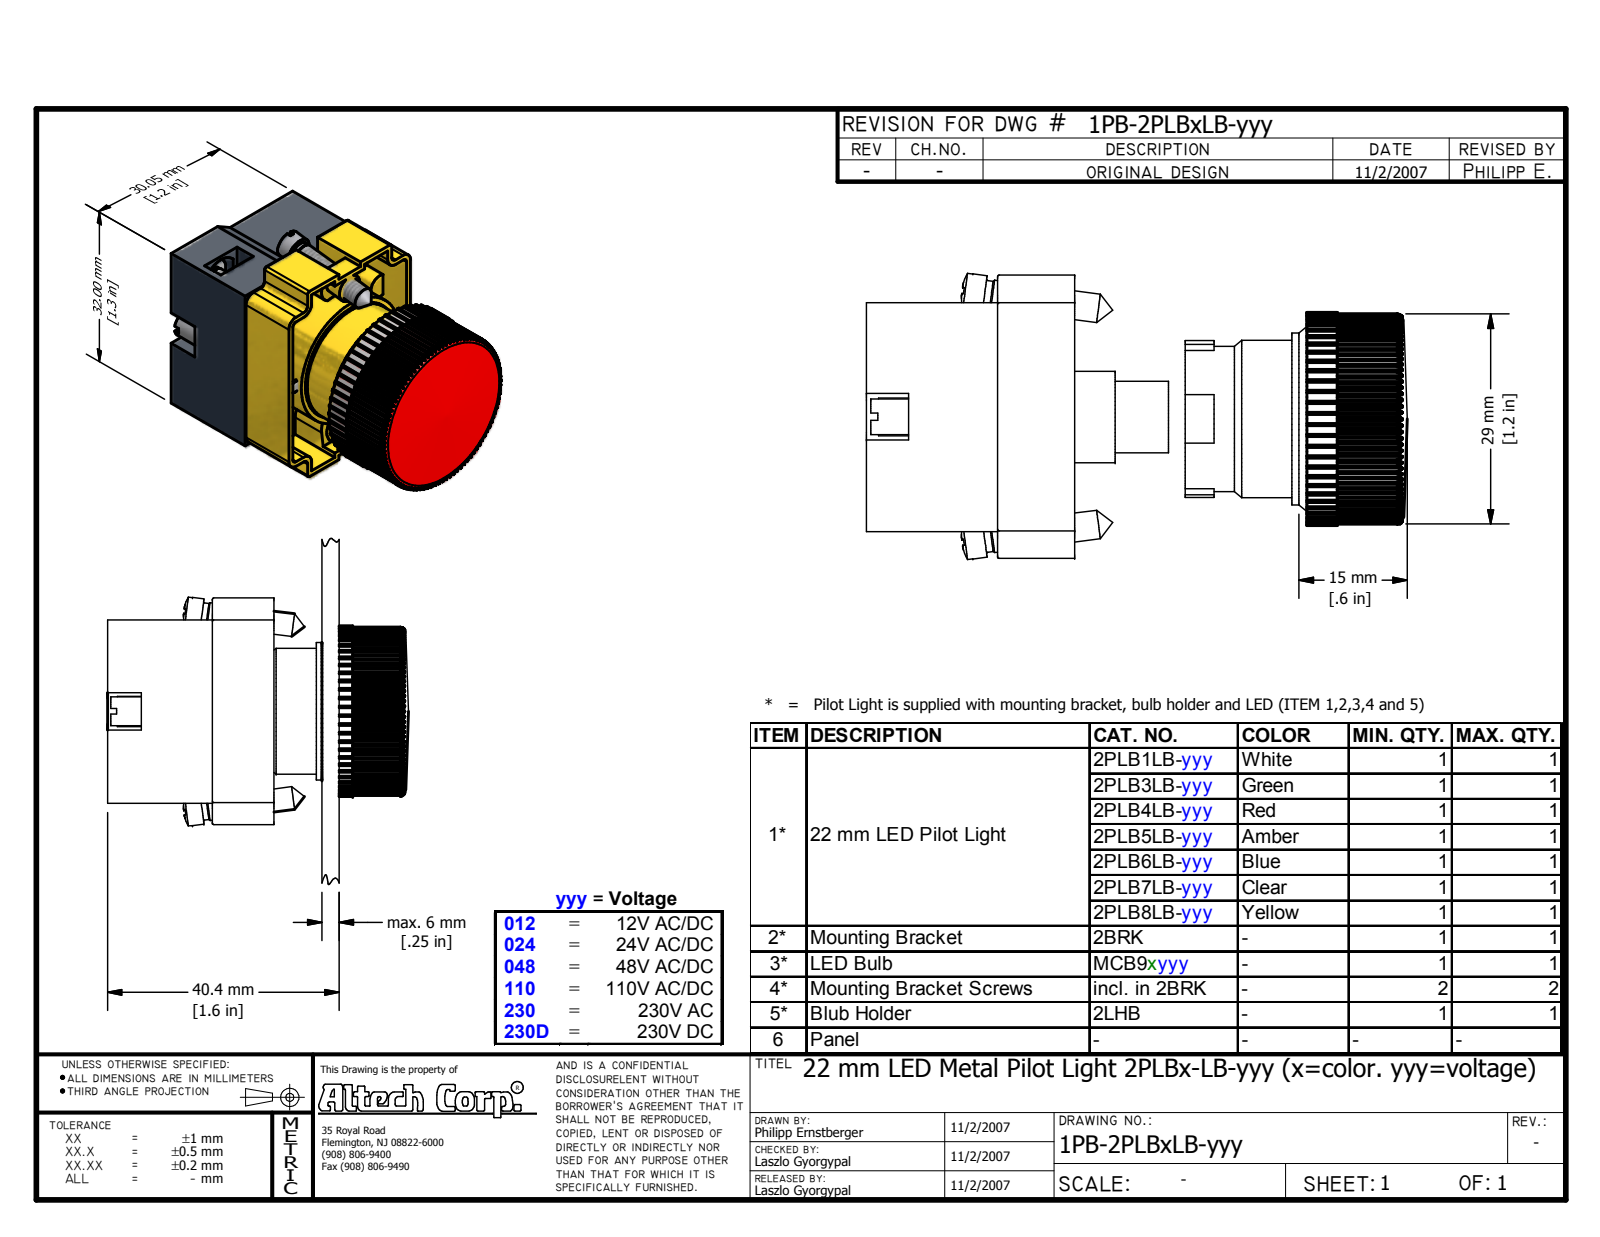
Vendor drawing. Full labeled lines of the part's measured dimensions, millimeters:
Part name (STEP PRODUCT): 2PLBxLB-yyy_assembly; 2BRK; DIN 7985 (Z) M4x18-Z; panel (+7 more)
STEP written by: Autodesk Inventor 2008 (AUTOMOTIVE_DESIGN)
Units: millimetres
Bodies: 12 solids, 992 faces (553 planar, 324 cylindrical, 115 other)
Overall size (bounding box): 60.45 × 52.5 × 45
Volume: 36 778 mm³ · Surface area: 27 396 mm²
Round holes (diameter × count): ⌀2.5 ×5, ⌀2.6 ×2, ⌀3 ×1, ⌀13.3 ×1, ⌀18 ×1, ⌀22 ×1, ⌀22.25 ×1, ⌀22.5 ×1, ⌀24 ×1
Round bosses / shafts (diameter × count): ⌀5 ×4, ⌀3 ×3, ⌀4 ×2, ⌀3.65 ×2, ⌀2.75 ×2, ⌀29.4 ×1, ⌀24.25 ×1, ⌀20.3 ×1
Partial cylindrical surfaces — rounded edges, fillets, slot ends (radius × count): R0.25 ×10, R0.72 ×8, R1 ×8, R2.25 ×5, R0.5 ×4, R0.8 ×4, R1.8 ×4, R2 ×4
Main face-to-face distances: 3, 1, 19.09, 22.09, 30, 18.3, 37.39, 40.39, 29, 19.3
Hole centre spacings: 14.53, 6.52, 6.57, 13, 25.88, 26, 26.27, 29.07
